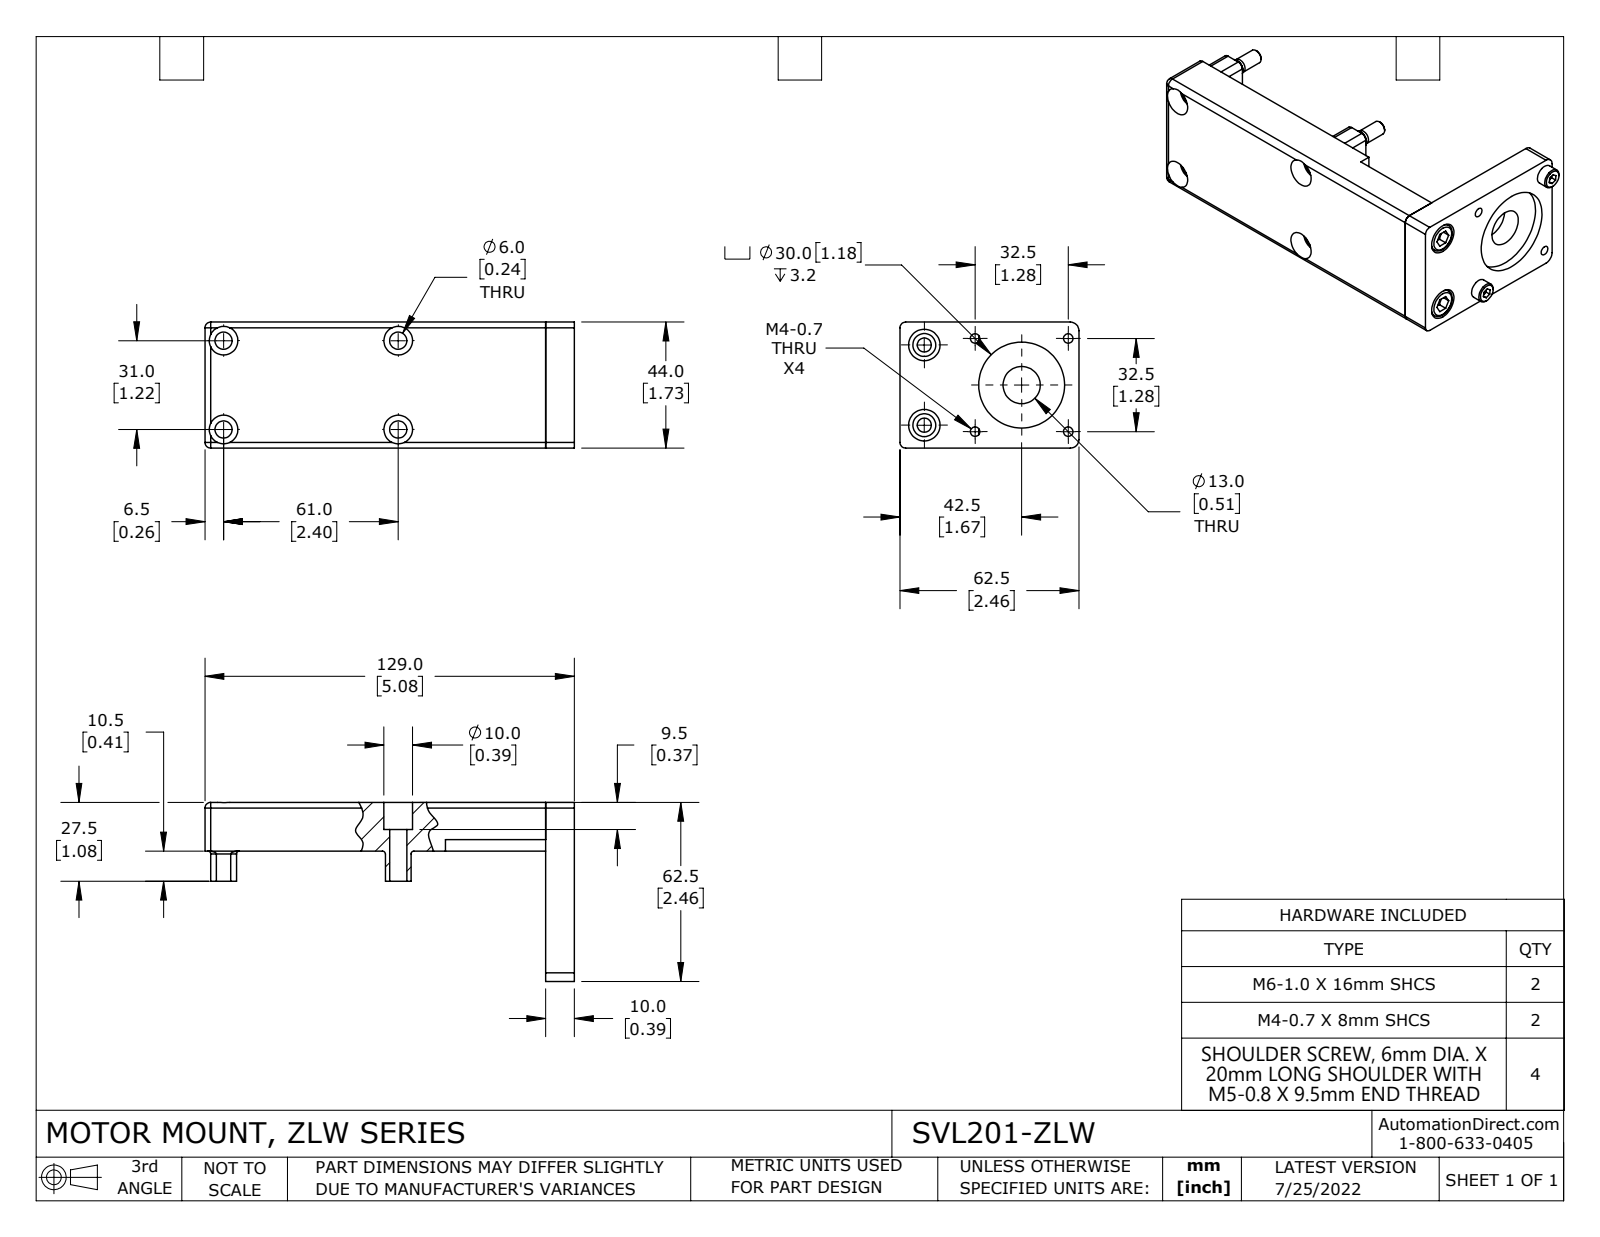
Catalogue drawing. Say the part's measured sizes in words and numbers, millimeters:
The part is named "SVL201-ZLW". Its 3-D file was written by "SolidWorks 2021 (CONFIG_CONTROL_DESIGN)". It is 12 solids with 396 faces: 129 planar, 137 cylindrical and 130 other. Overall it measures 133 by 62.5 by 44 millimeters. Its volume is 118 285 cubic millimeters and its surface area 35 570 square millimeters. Round holes: 6 of diameter 6, 4 of diameter 3.3, 4 of diameter 10, 2 of diameter 4, 2 of diameter 4.92, 2 of diameter 8, 2 of diameter 11, 1 of diameter 13, 1 of diameter 30. Round bosses or shafts: 4 of diameter 5.96, 4 of diameter 5, 4 of diameter 4.02, 2 of diameter 10, 2 of diameter 7, 2 of diameter 4. Partial cylindrical surfaces (rounded edges, fillets, slot ends): 13 of radius 2, 6 of radius 1, 2 of radius 3. The main face-to-face distances are 17, 44, 10, 61, 9, 119, 2, 129, 10.5, 27.5. The hole center spacings are 15.5, 23, 32.52, 62.94, 61, 17.88, 31, 35.08.
